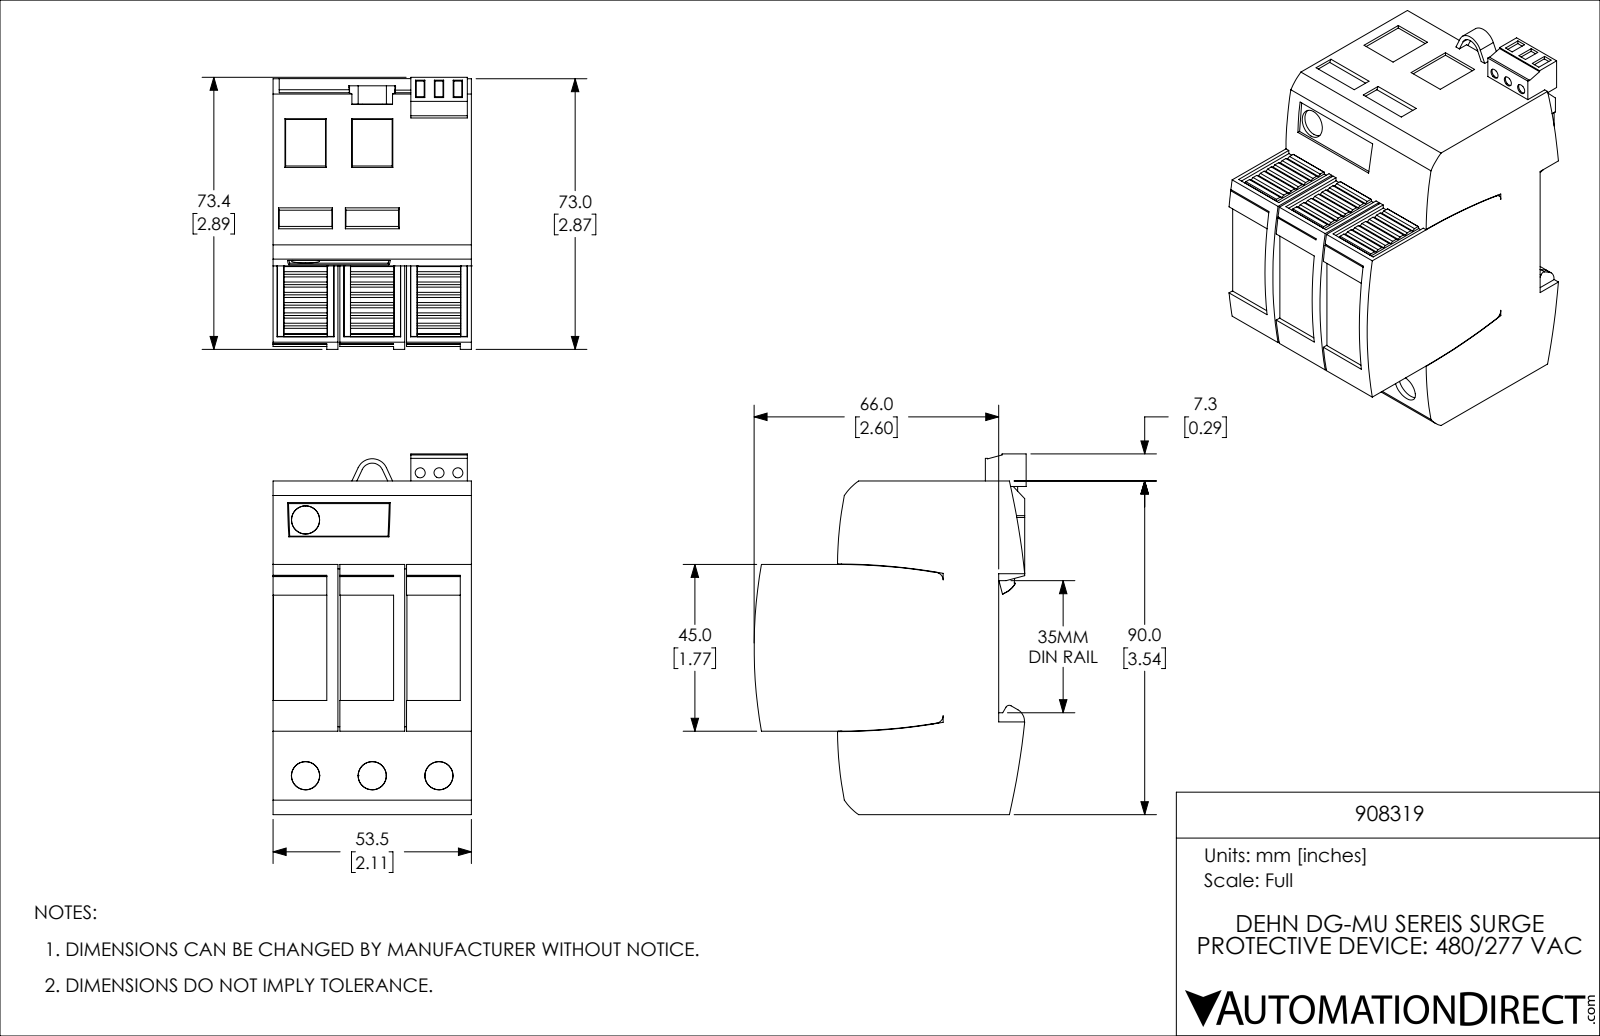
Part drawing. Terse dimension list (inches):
name: 908319
written by: SolidWorks 2019 (CONFIG_CONTROL_DESIGN)
unit: in
bodies: 1 solid, 672 faces (506 planar, 128 cylindrical, 38 other)
size: 3.831 × 2.89 × 2.106
volume: 16.59 in³; area: 55.39 in²
holes: 3× ⌀0.106
rounds: 12× R0.004, 12× R0.047, 3× R0.02, 2× R0.008, 2× R0.016, 2× R0.03, 2× R0.079, 2× R0.079
face distances: 0.709, 2.106, 0.685, 0.689, 1.417, 1.398, 1.394, 3.543, 0.024, 2.518
hole spacings: 0.2, 0.4
